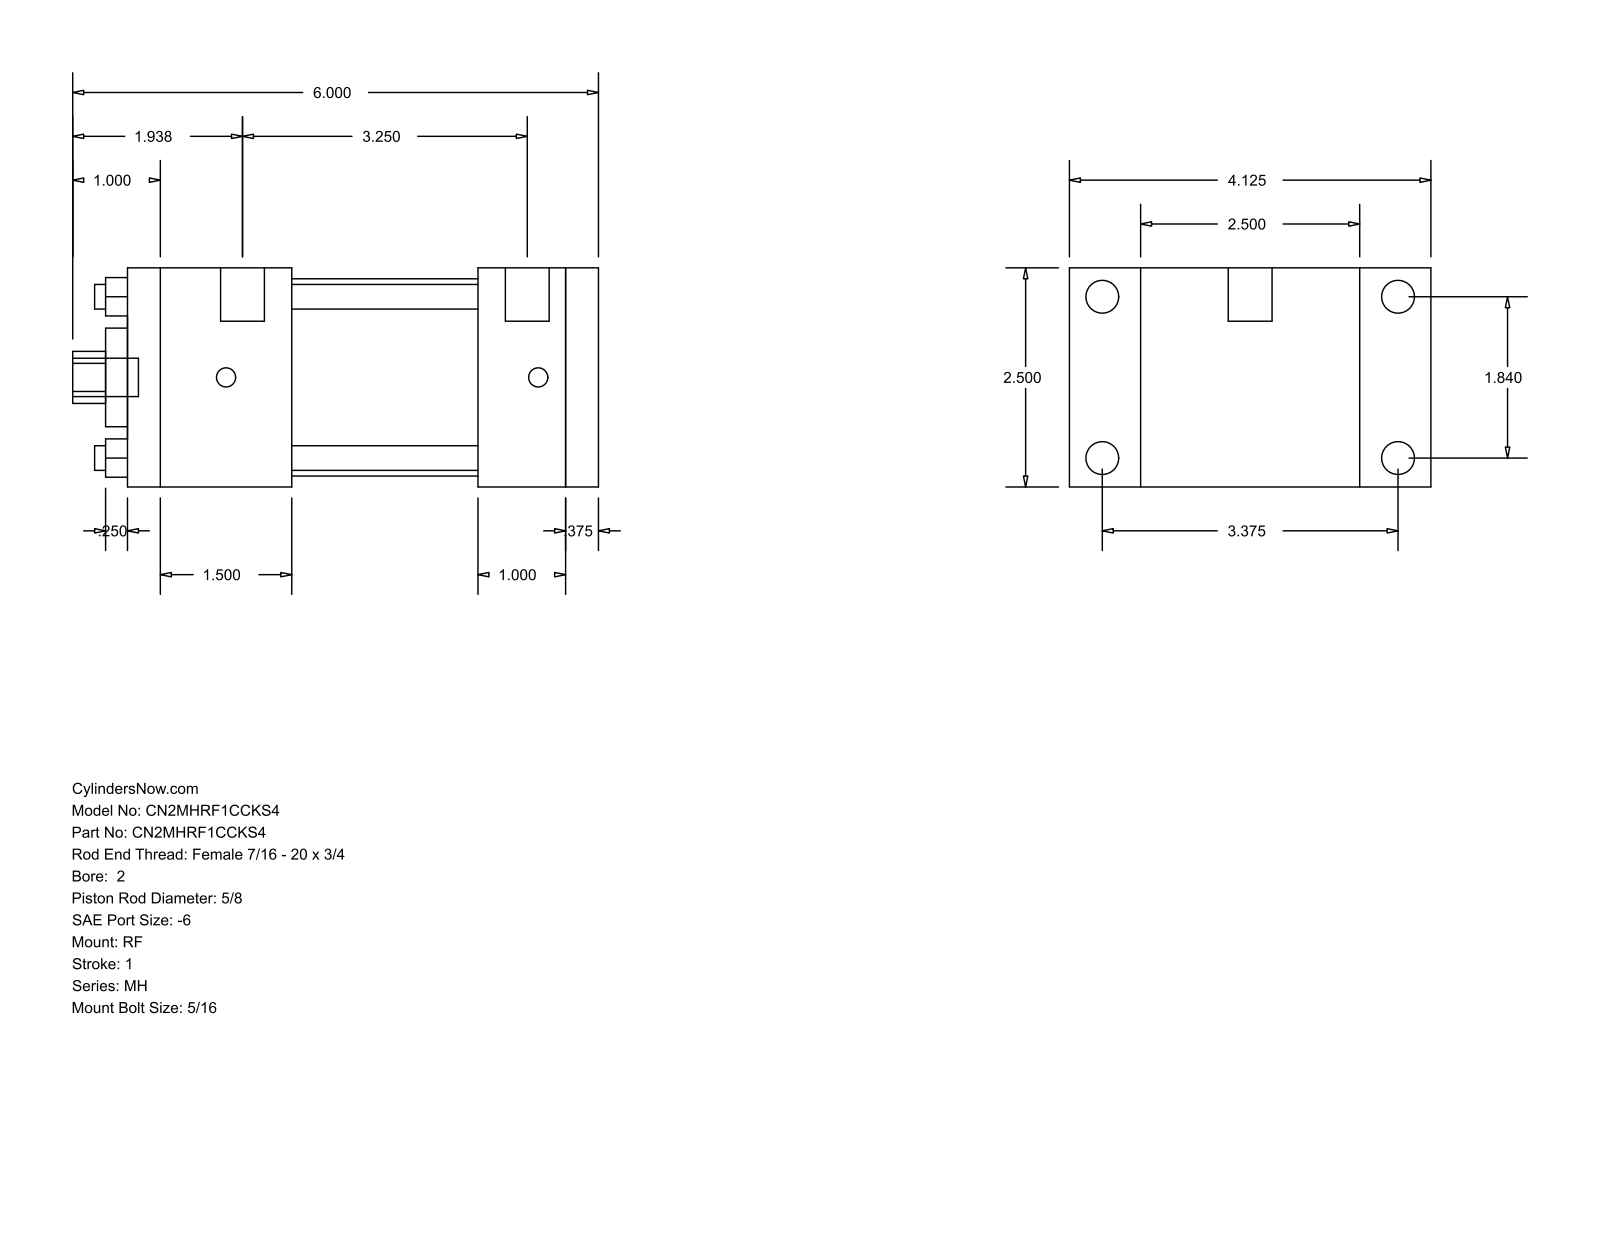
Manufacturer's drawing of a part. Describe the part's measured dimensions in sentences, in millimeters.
The part is named "MH_RF__0200_0.625". Its 3-D file was written by "GSSL Pune (CONFIG_CONTROL_DESIGN)". It is 0 solids with 92 faces: 64 planar, 28 cylindrical and 0 other. Overall it measures 152.4 by 104.78 by 63.5 millimeters. Round holes: 4 of diameter 7.14, 1 of diameter 15.88, 1 of diameter 28.57, 1 of diameter 57.15. Round bosses or shafts: 4 of diameter 9.53, 4 of diameter 5.56, 2 of diameter 12.7, 1 of diameter 11.11. Partial cylindrical surfaces (rounded edges, fillets, slot ends): 1 of radius 7.54. The main face-to-face distances are 63.5, 136.52, 9.52, 127, 53.97, 47.62, 101.59, 79.38, 88.9, 25.41. The hole center spacings are 33.05, 46.74, 66.1.
